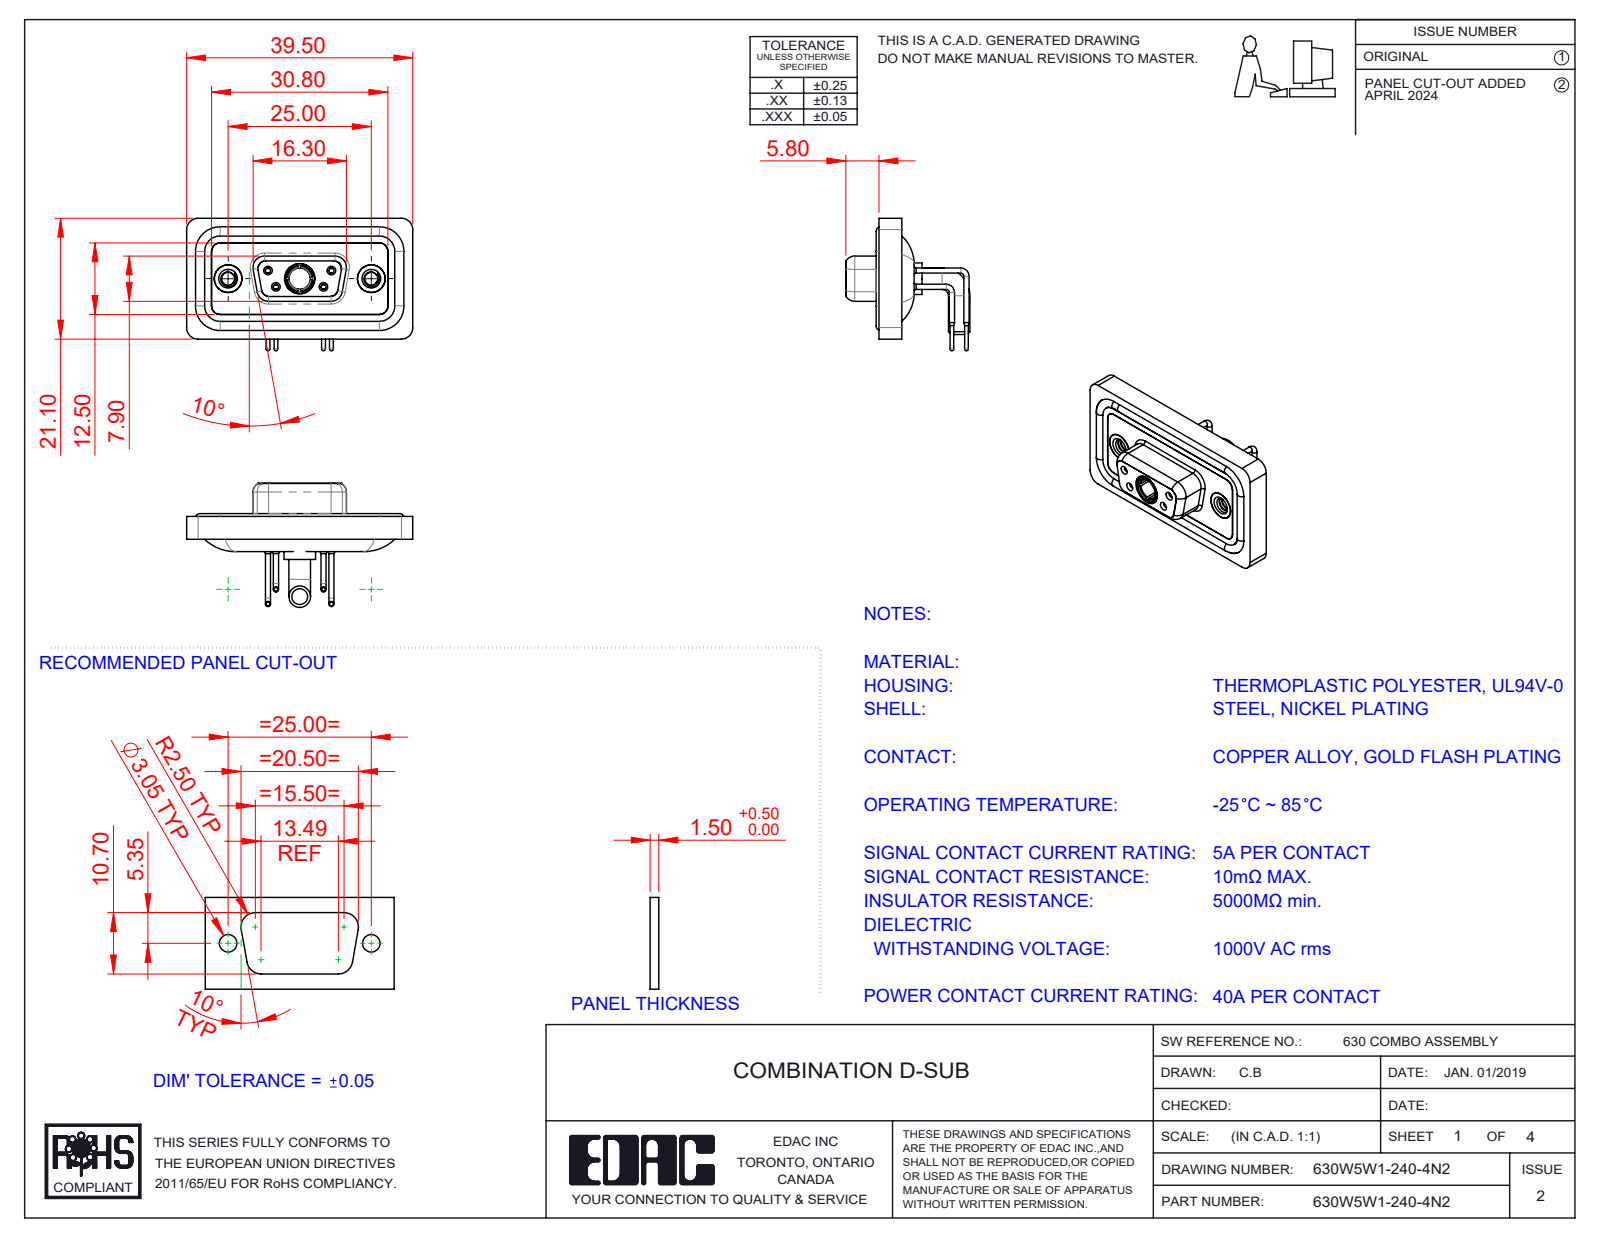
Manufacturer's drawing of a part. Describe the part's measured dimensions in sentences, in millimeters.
The part is named "630Combo Contact Row 1_50 Contacts; Power Socket_40A RA; 630Combo Waterproof Housing_09 Contacts; 630Combo Housing_5W1 (+5 more)". Its 3-D file was written by "SolidWorks 2023 (CONFIG_CONTROL_DESIGN)". It is 13 solids with 676 faces: 194 planar, 305 cylindrical and 177 other. Overall it measures 39.5 by 23.12 by 21.68 millimeters. Its volume is 4 901 cubic millimeters and its surface area 7 887 square millimeters. Round holes: 4 of diameter 0.9, 4 of diameter 1.1, 4 of diameter 1.5, 4 of diameter 2, 3 of diameter 4.85, 2 of diameter 1.6, 2 of diameter 1.7, 2 of diameter 2.26, 2 of diameter 4, 2 of diameter 4.05, 2 of diameter 5, 1 of diameter 3.7. Round bosses or shafts: 6 of diameter 1.6, 4 of diameter 0.9, 4 of diameter 0.65, 2 of diameter 4.95, 2 of diameter 4.8, 2 of diameter 3.75, 1 of diameter 5.5, 1 of diameter 5.2. Partial cylindrical surfaces (rounded edges, fillets, slot ends): 18 of radius 1.5, 18 of radius 2, 8 of radius 1.35, 8 of radius 1.6, 4 of radius 0.25, 4 of radius 0.5, 4 of radius 0.6, 4 of radius 0.65. The main face-to-face distances are 0.4, 1.8, 1.1, 2.9, 2.5, 1.6, 3.1, 2.1, 1.5, 0.5. The hole center spacings are 3.16, 5.72, 7.1, 12.5, 18.1, 4.39, 4.4, 8.31.
